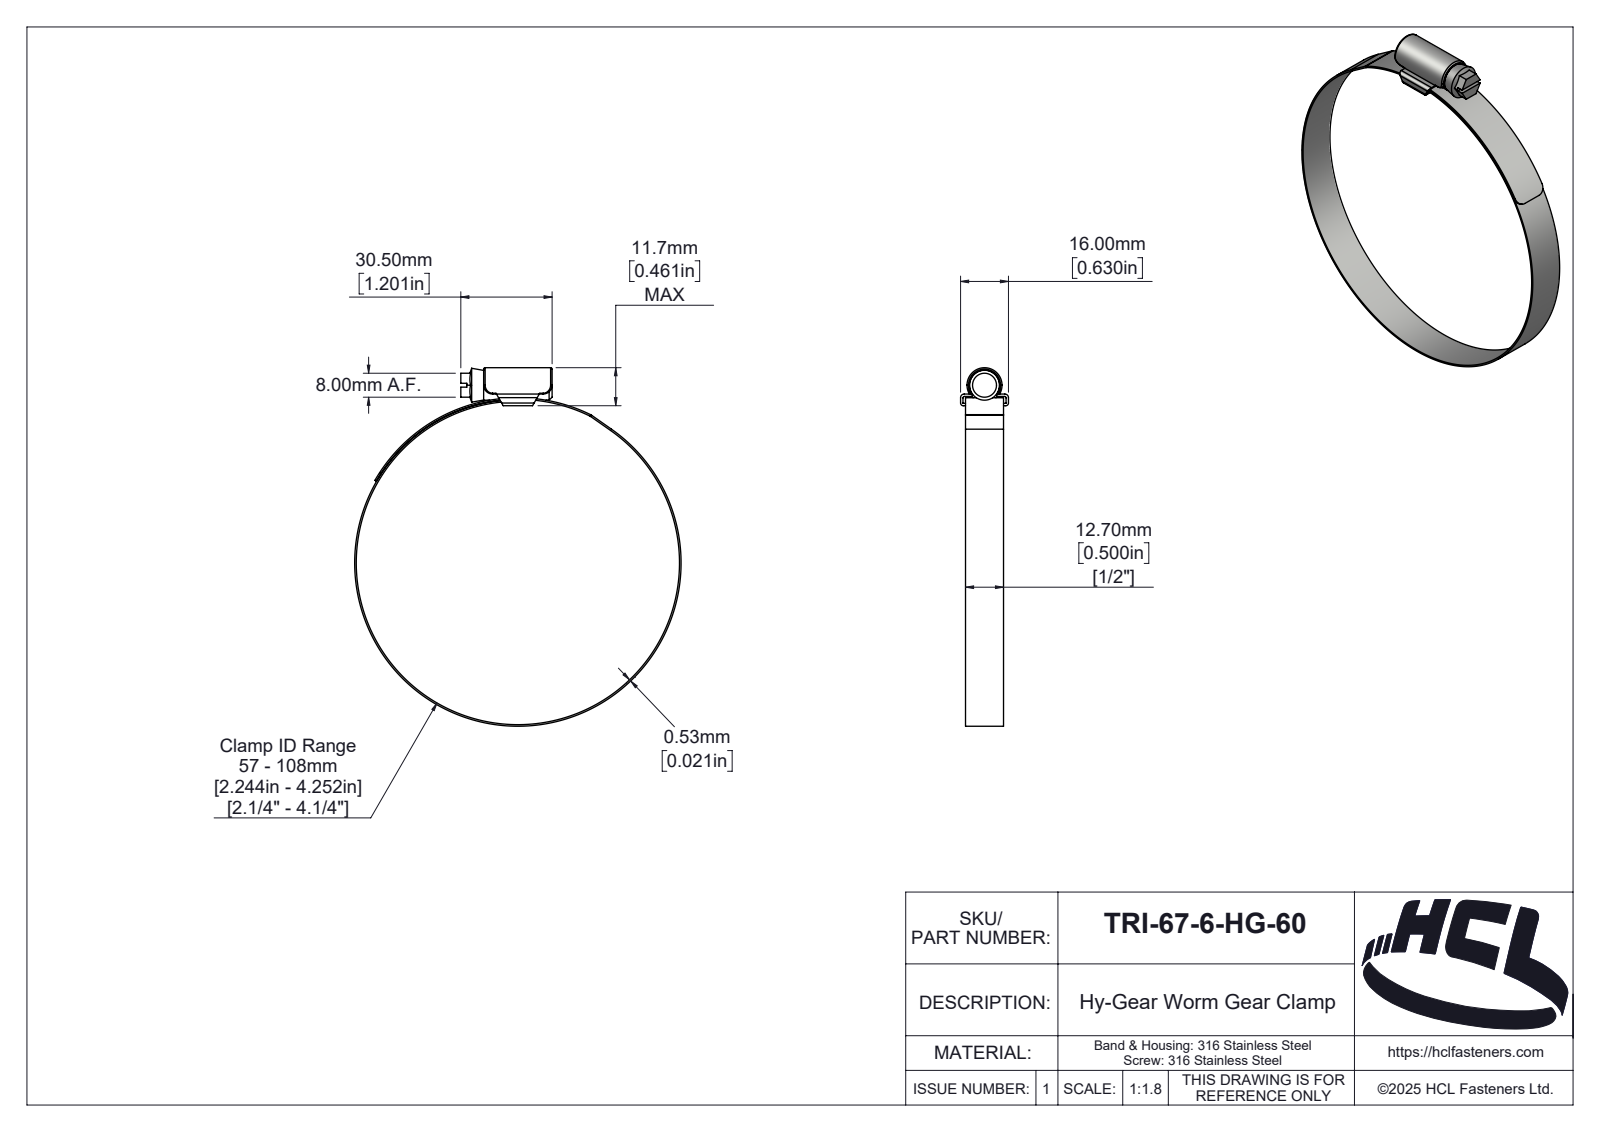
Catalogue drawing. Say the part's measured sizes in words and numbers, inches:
The part is named "TRI-57-0-HG-60". Its 3-D file was written by "SolidWorks 2025 (AUTOMOTIVE_DESIGN)". It is 3 solids with 189 faces: 39 planar, 89 cylindrical and 61 other. Overall it measures 4.714 by 4.294 by 0.63 inches. Its volume is 0.346 cubic inches and its surface area 20.86 square inches. Round holes: 1 of diameter 4.252. Round bosses or shafts: 1 of diameter 4.294, 1 of diameter 0.394. Partial cylindrical surfaces (rounded edges, fillets, slot ends): 6 of radius 0.02, 4 of radius 0.118, 2 of radius 0.004, 2 of radius 0.035, 2 of radius 0.047, 1 of radius 0.018, 1 of radius 0.074, 1 of radius 0.079. The main face-to-face distances are 0.031, 0.5, 0.122, 0.021, 0.091, 0.154, 1.201, 0.065, 0.565, 0.598.
